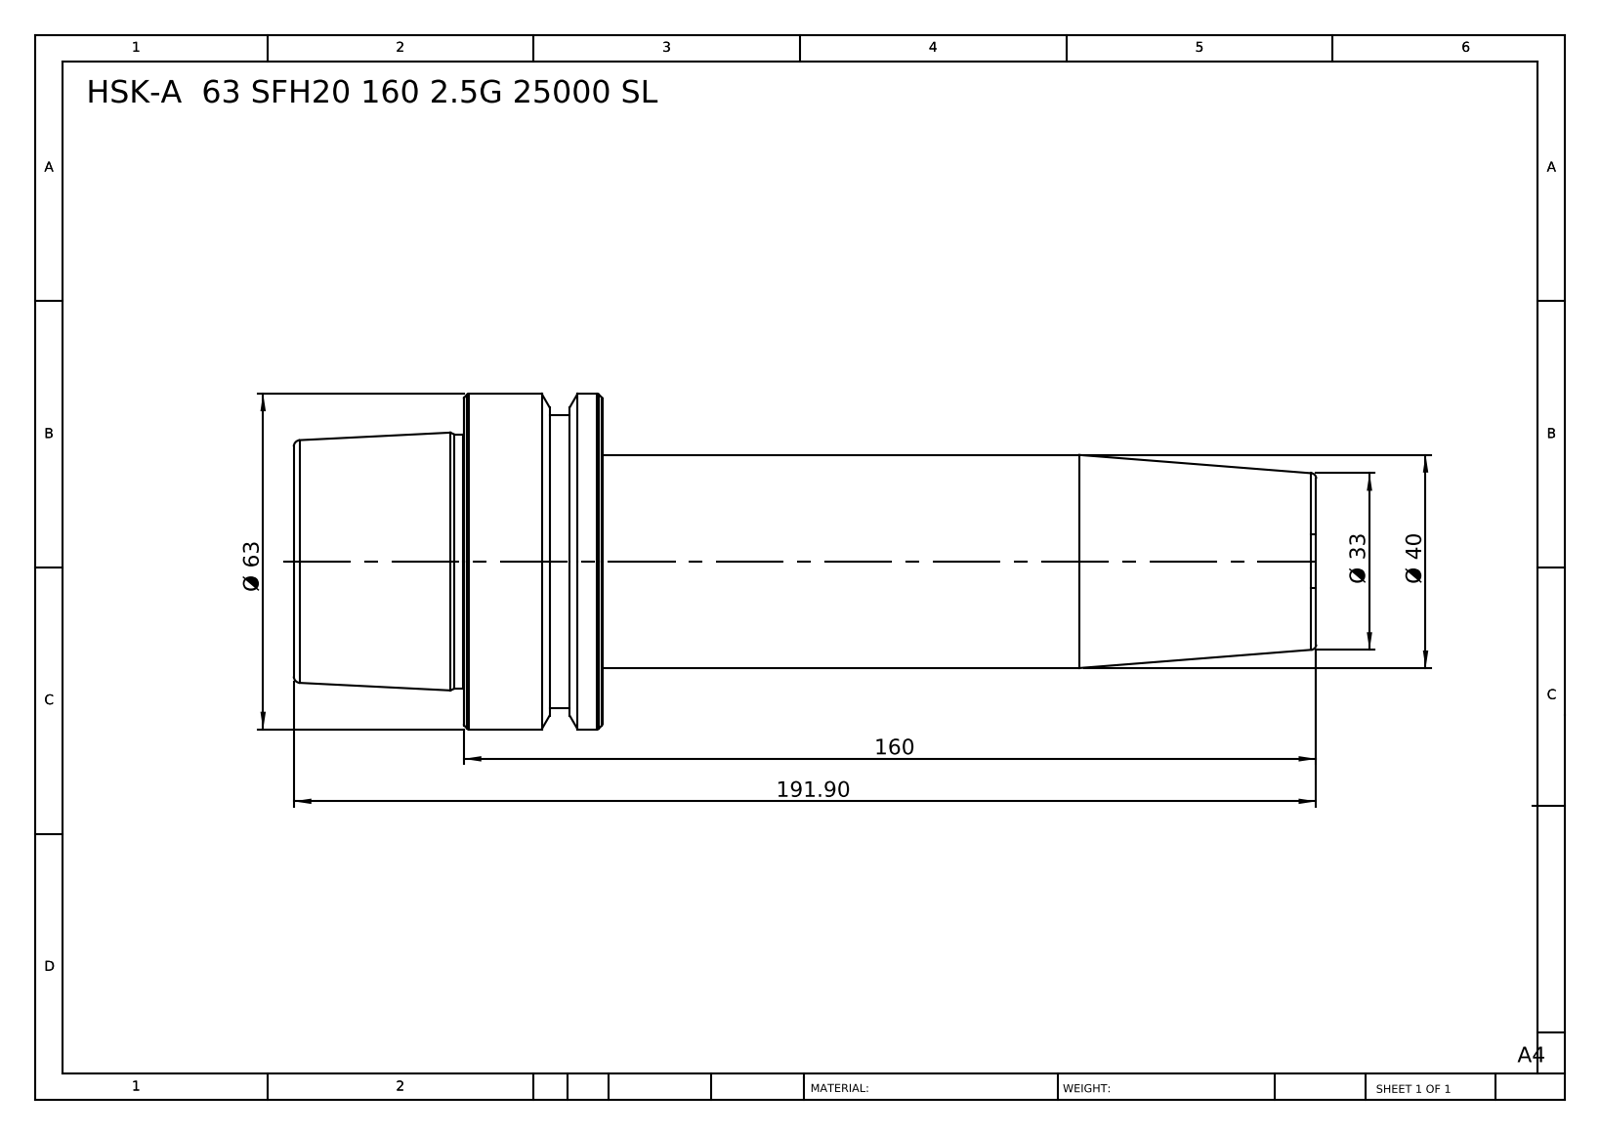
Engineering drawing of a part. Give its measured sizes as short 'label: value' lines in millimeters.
name: HSK-A 63 SFH20 160 2.5G 25000 SL
written by: SolidWorks 2014 (CONFIG_CONTROL_DESIGN)
unit: mm
bodies: 1 solid, 46 faces (6 planar, 10 cylindrical, 30 other)
size: 191.9 × 63 × 63
volume: 291 758 mm³; area: 32 576 mm²
bosses: 1× ⌀63, 1× ⌀55, 1× ⌀47.78, 1× ⌀40
face distances: 57.9, 134, 191.9, 160, 26, 31.9, 140.1, 6.1, 19.9, 51.8
